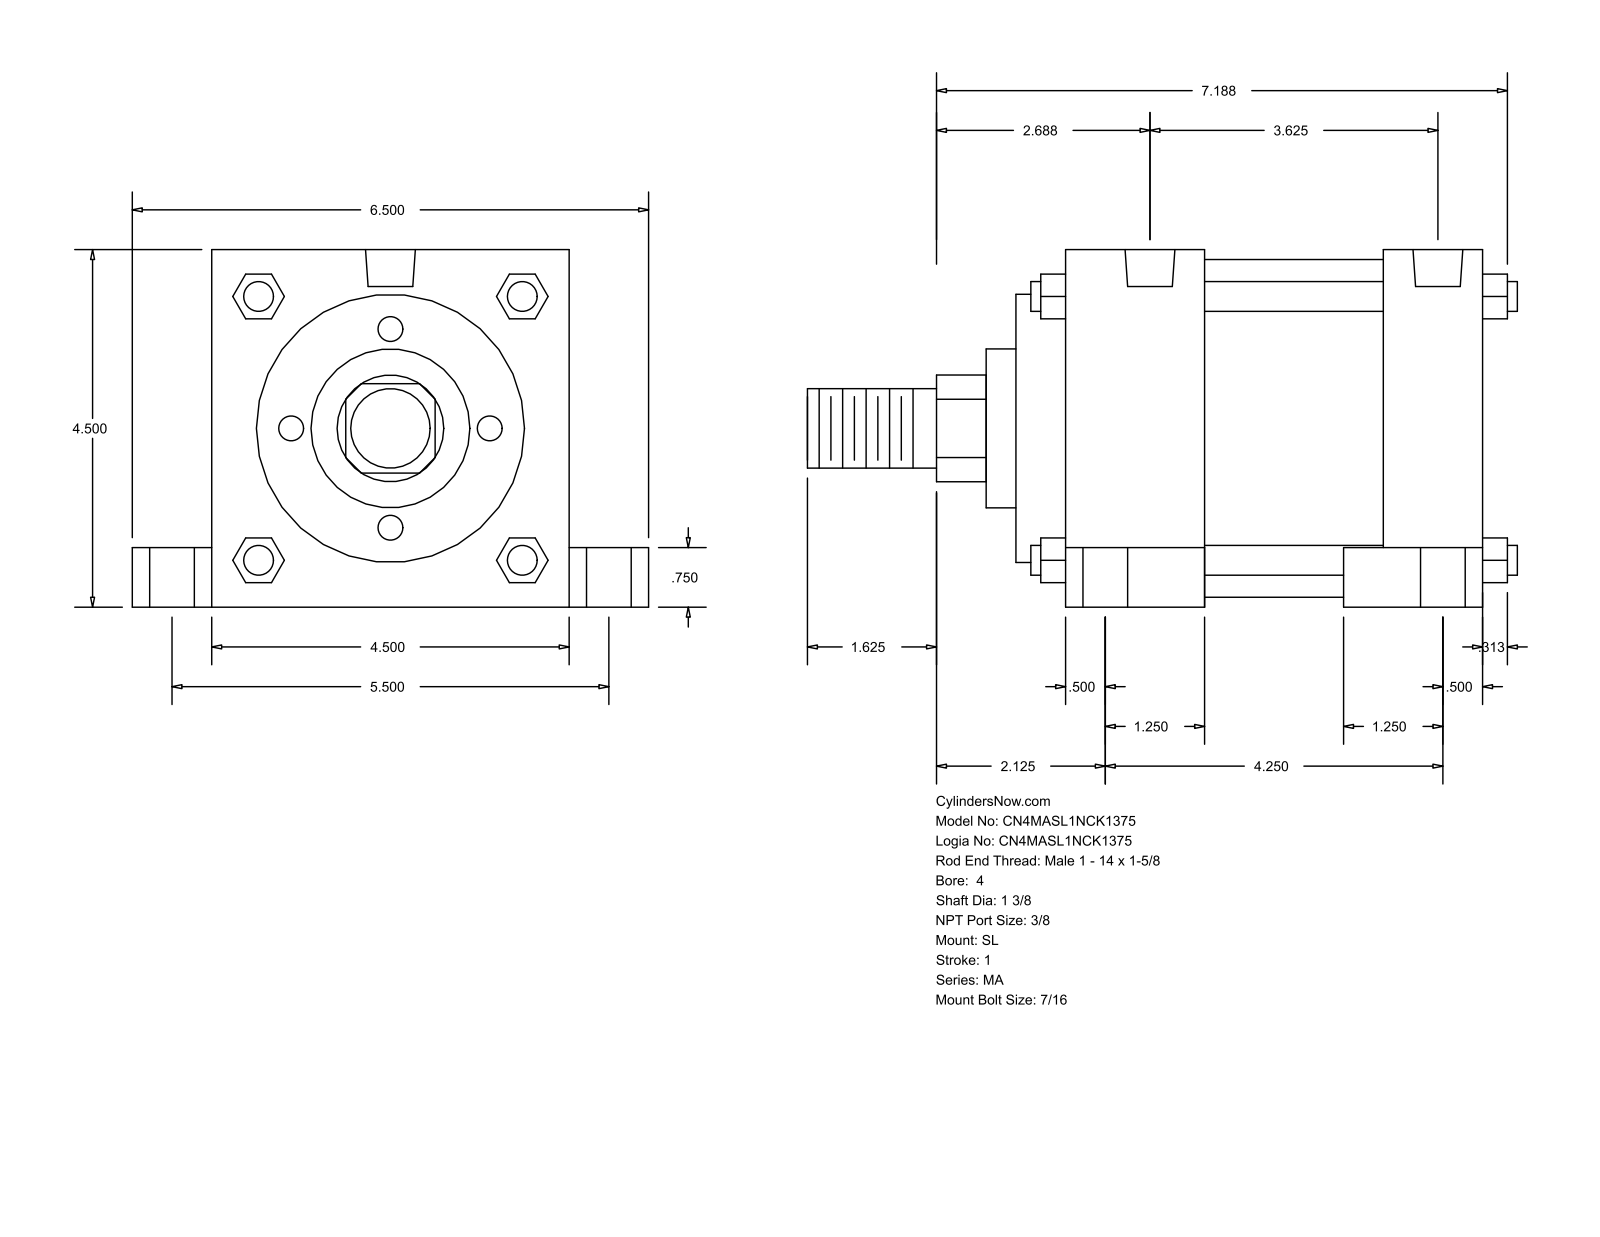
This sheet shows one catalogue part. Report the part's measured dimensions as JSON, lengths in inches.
{"part_name": "MA_SL__0400_1.375", "step_written_by": "GSSL Pune (CONFIG_CONTROL_DESIGN)", "units": "inches", "bodies": {"solids": 0, "faces": 150, "planar": 113, "cylindrical": 37, "other": 0}, "overall_size": [8.937, 6.5, 4.5], "round_holes": [[0.437, 4], [0.563, 4], [0.813, 4], [0.627, 2]], "round_bosses_or_shafts": [[0.375, 4], [4.25, 1], [3.375, 1], [2, 1], [1.375, 1], [1, 1]], "partial_cylinders_radius": [[0.672, 1]], "face_to_face_distances": [4.5, 5.25, 5.875, 0.625, 2.375, 1.75, 3.5, 4.625, 4, 2.25], "hole_center_spacings": [0.188, 2.751, 2.761, 2.807, 2.85, 3.25, 3.437, 4.25]}
